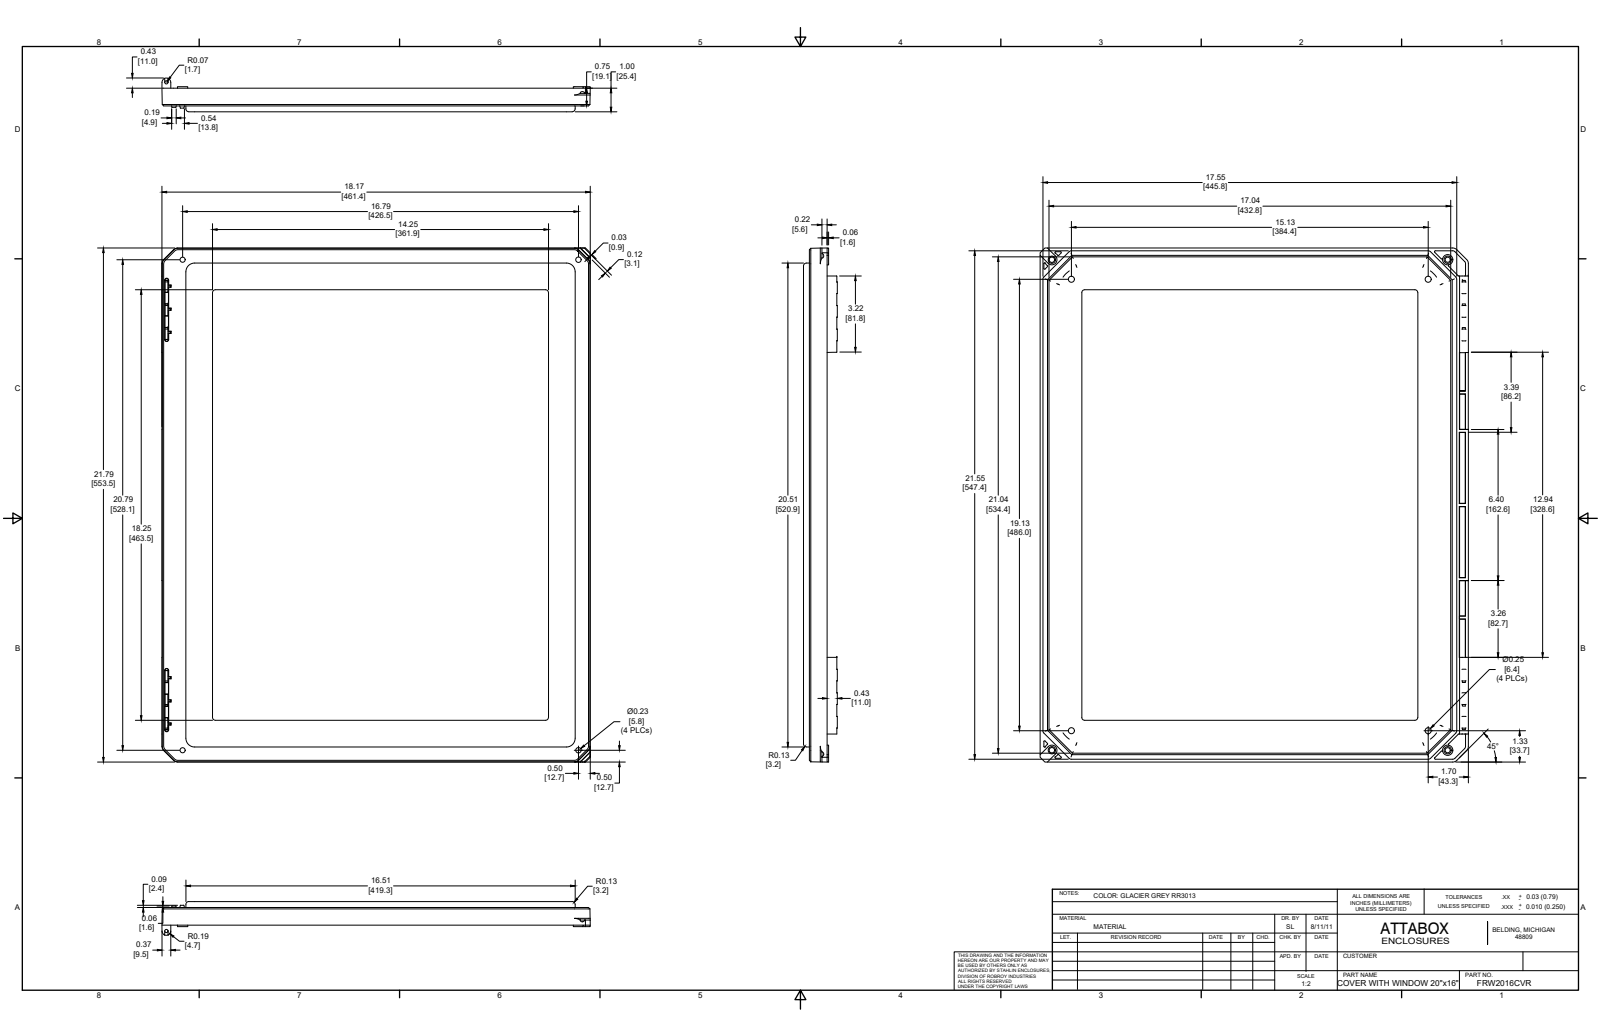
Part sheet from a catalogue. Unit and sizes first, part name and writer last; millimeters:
Units: millimetres
Overall size (bounding box): 553.5 × 461.4 × 36.4
Round holes (diameter × count): ⌀6.4 ×4, ⌀5.6 ×2, ⌀5.8 ×2, ⌀8 ×2, ⌀3.5 ×1
Round bosses / shafts (diameter × count): ⌀11 ×2
Partial cylindrical surfaces — rounded edges, fillets, slot ends (radius × count): R0.8 ×27, R0.3 ×18, R1.6 ×18, R2.4 ×16, R3.2 ×16, R1 ×10, R1.5 ×9, R0.1 ×8
Main face-to-face distances: 3.2, 6.4, 3.2, 19.1, 9.5, 9.5, 25.4, 15.9, 22.2, 15.9
Hole centre spacings: 507.5, 29.8, 29.8, 384.4, 406, 406, 426.5, 486
Volume: 642 700 mm³ · Surface area: 298 300 mm²
Bodies: 1 solid, 630 faces (274 planar, 204 cylindrical, 152 other)
Part name (STEP PRODUCT): FRW2016CVR
STEP written by: SolidWorks 2019 (AUTOMOTIVE_DESIGN)
